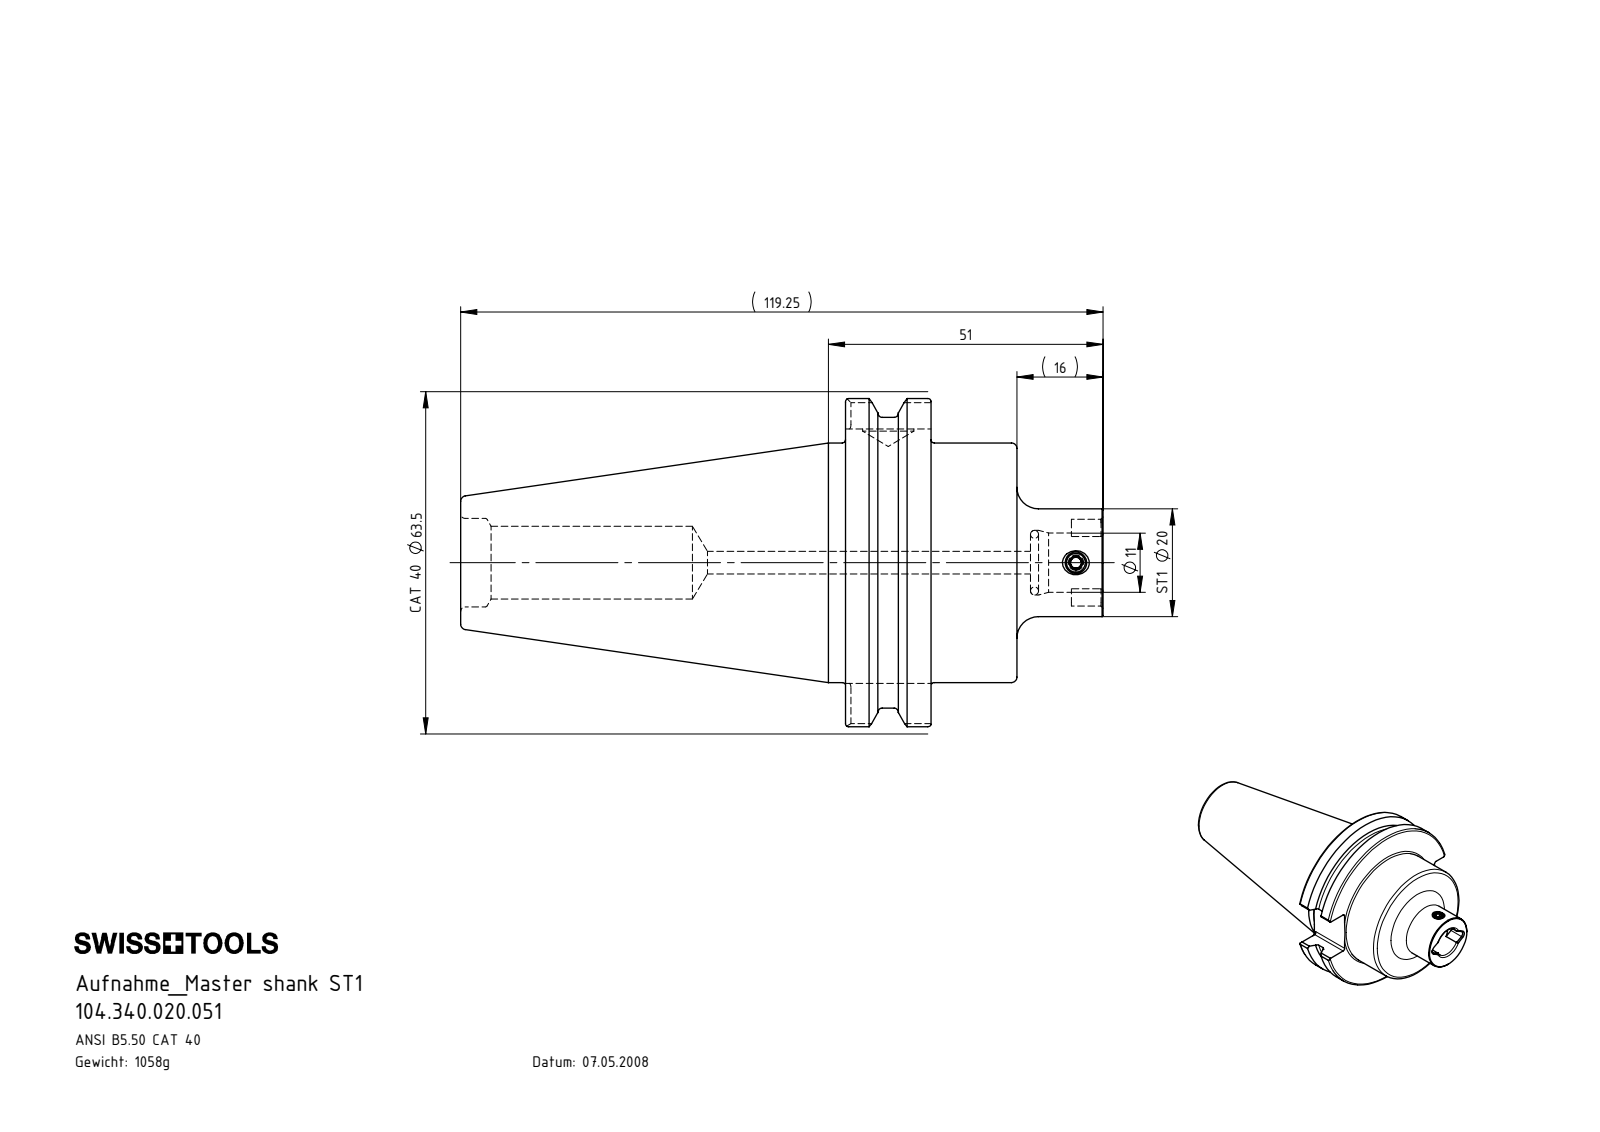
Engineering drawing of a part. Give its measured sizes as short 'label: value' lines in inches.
name: ST1-ER1.001.005_A; DIN 3771 - 9x1.5; CT4-ST1.K01.051; CT4-ST1.K01.051_A
written by: SolidWorks 2015 (CONFIG_CONTROL_DESIGN)
unit: in
bodies: 3 solids, 144 faces (44 planar, 39 cylindrical, 61 other)
size: 4.695 × 2.5 × 2.396
volume: 8.23 in³; area: 35.61 in²
holes: 1× ⌀0.138, 1× ⌀0.165, 1× ⌀0.374, 1× ⌀0.433, 1× ⌀0.472, 1× ⌀0.531, 1× ⌀0.647
bosses: 1× ⌀2.5, 1× ⌀2.219, 1× ⌀1.75, 1× ⌀0.787, 1× ⌀0.157
rounds: 8× R0.031, 2× R0.051
face distances: 0.625, 1.253, 0.628, 1.858, 1.883, 1.258, 0.63, 2.812, 3.437, 4.065
